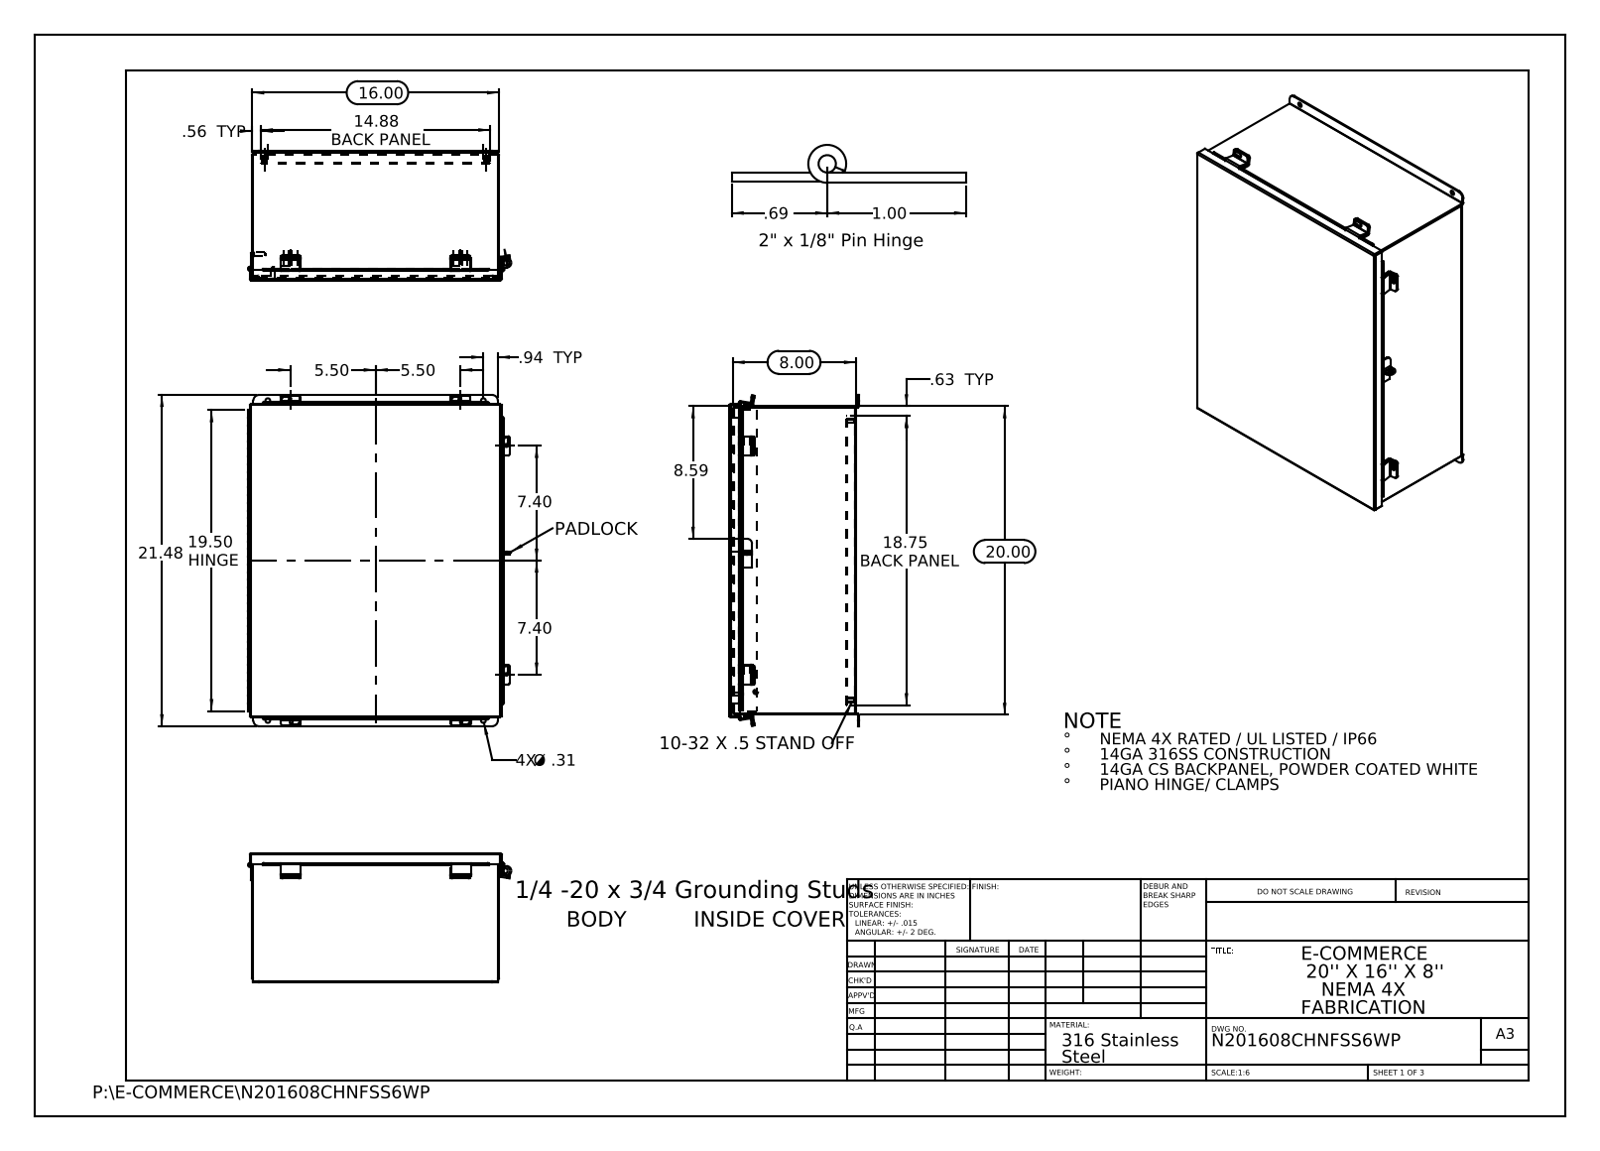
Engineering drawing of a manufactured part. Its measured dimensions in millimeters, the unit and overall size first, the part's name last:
Units: millimetres
Overall size (bounding box): 545.5 × 433.6 × 213.1
Round holes (diameter × count): ⌀6.4 ×10, ⌀4.7 ×4, ⌀7.9 ×4, ⌀3.2 ×1, ⌀3.2 ×1, ⌀9.5 ×1, ⌀9.5 ×1
Round bosses / shafts (diameter × count): ⌀8 ×4, ⌀8 ×2, ⌀6 ×2, ⌀6.9 ×1, ⌀6.4 ×1
Partial cylindrical surfaces — rounded edges, fillets, slot ends (radius × count): R3.2 ×24, R0.3 ×13, R0.2 ×12, R2.2 ×12, R3.4 ×12, R2.1 ×6, R2.5 ×6, R9.5 ×4
Main face-to-face distances: 1.9, 206.5, 204.5, 208.4, 404.5, 193.8, 14.6, 12.7, 191.8, 16.5
Hole centre spacings: 33.4, 361.6, 493.4, 610.8, 279.4, 355, 365.1, 460.4
Volume: 2 025 000 mm³ · Surface area: 2 164 000 mm²
Bodies: 27 solids, 938 faces (579 planar, 339 cylindrical, 20 other)
Part name (STEP PRODUCT): HW-CLH-JH-20104; N201608CHNFSS6WP Hinge Cover Side JIC; HW-CLH-JH-20154; N201608CHNFSS6WP Hinge Body Side (+8 more)
STEP written by: SolidWorks 2013 (CONFIG_CONTROL_DESIGN)
